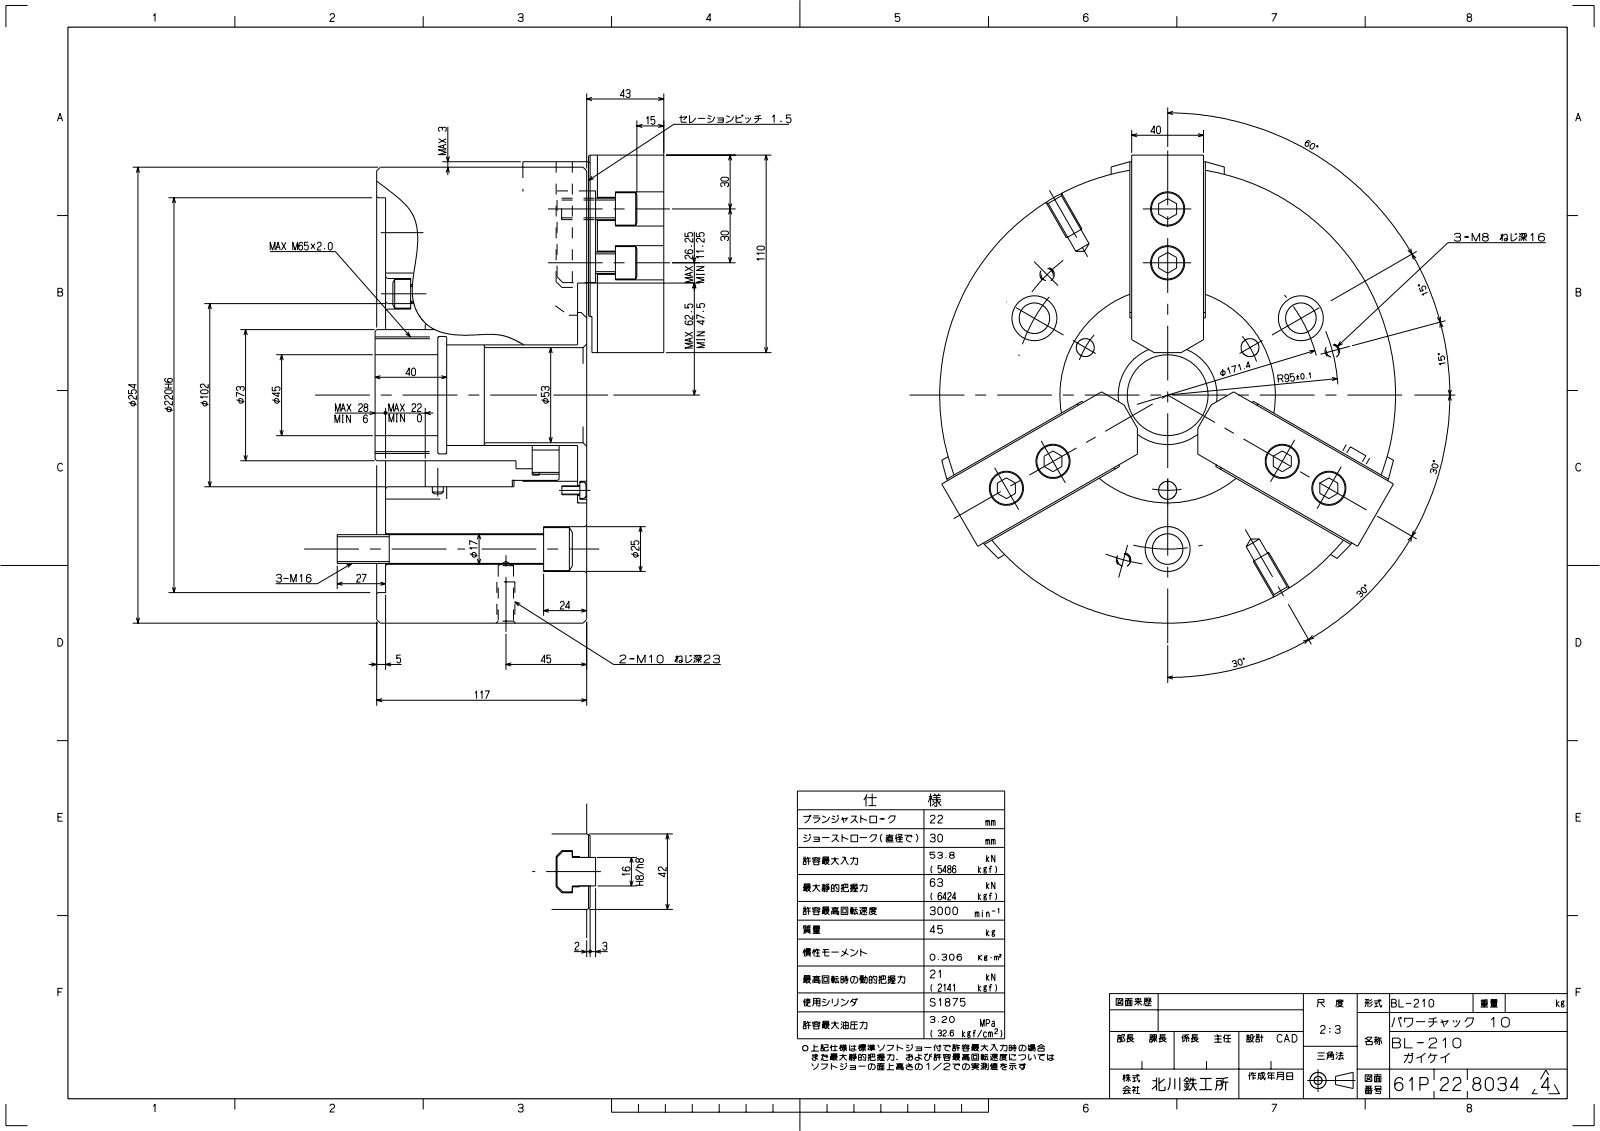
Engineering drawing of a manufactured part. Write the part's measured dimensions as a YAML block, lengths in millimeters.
part_name: "BL210-Solid"
step_written_by: "ST-DEVELOPER v16.7 (AUTOMOTIVE_DESIGN)"
units: millimeters
bodies: {solids: 1, faces: 3366, planar: 2441, cylindrical: 763, other: 162}
overall_size: [254, 254, 182.2]
volume: 5788000
surface_area: 427325
round_holes:
  - {diameter: 10.3, count: 6}
  - {diameter: 13, count: 6}
  - {diameter: 19, count: 6}
  - {diameter: 4.2, count: 3}
  - {diameter: 5.5, count: 3}
  - {diameter: 6.8, count: 3}
  - {diameter: 10, count: 3}
  - {diameter: 17, count: 3}
  - {diameter: 25, count: 3}
  - {diameter: 8.5, count: 1}
  - {diameter: 45, count: 1}
  - {diameter: 53, count: 1}
round_bosses_or_shafts:
  - {diameter: 18, count: 6}
  - {diameter: 11.7, count: 6}
  - {diameter: 24, count: 3}
  - {diameter: 15.68, count: 3}
  - {diameter: 9.5, count: 3}
  - {diameter: 4.83, count: 3}
  - {diameter: 254, count: 1}
  - {diameter: 95, count: 1}
partial_cylinders:
  - {radius: 0.1, count: 138}
  - {radius: 0.8, count: 9}
  - {radius: 11.5, count: 6}
  - {radius: 8.5, count: 3}
  - {radius: 5, count: 2}
  - {radius: 0.51, count: 1}
  - {radius: 2.19, count: 1}
  - {radius: 4.08, count: 1}
face_to_face_distances: [112, 5, 117, 40, 160.2, 155.2, 43.2, 12, 118.2, 6.2]
hole_center_spacings: [91.44, 121.25, 60.72, 77.83, 77.84, 141.52, 25.32, 30]
